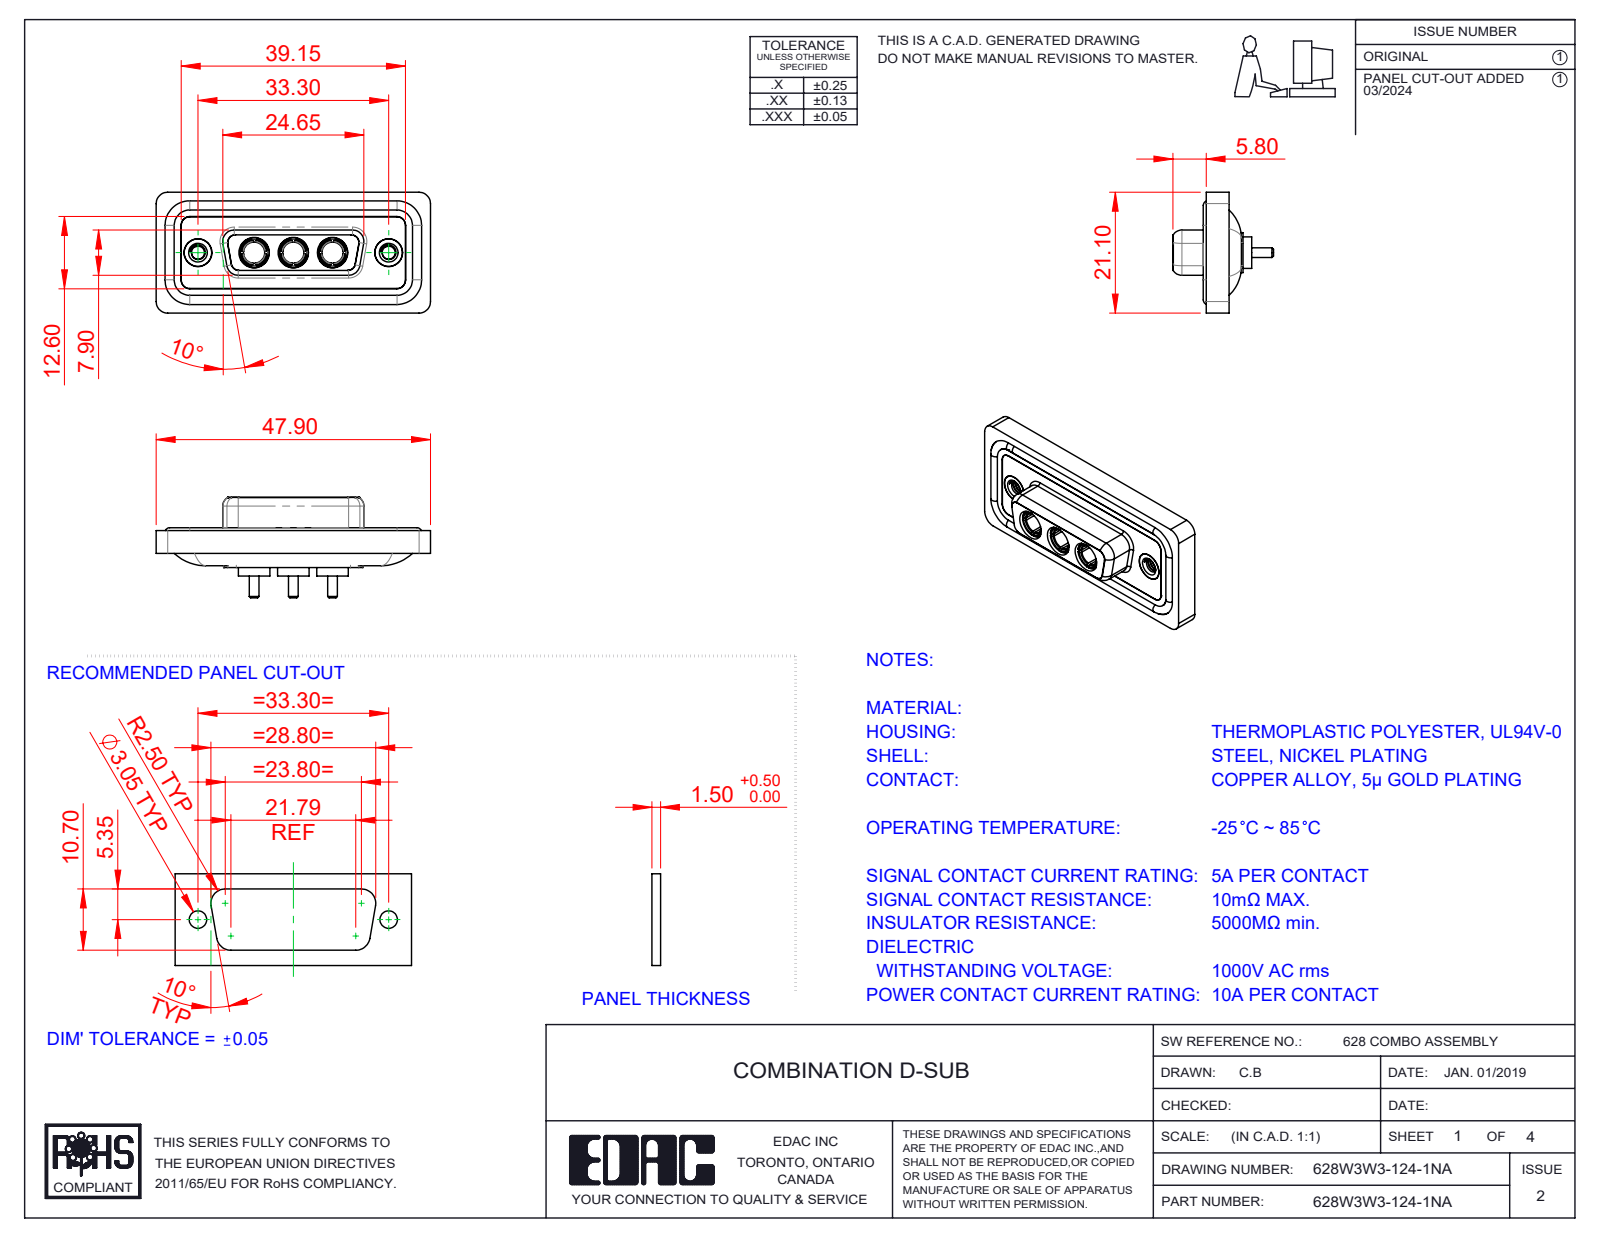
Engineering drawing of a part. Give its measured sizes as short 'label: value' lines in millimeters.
name: 628Combo Threaded Rivet_A; 628Combo Housing_3W3; 628Combo Waterproof Housing_15 Contacts; 628W3W3-124-1NA (+3 more)
written by: SolidWorks 2023 (CONFIG_CONTROL_DESIGN)
unit: mm
bodies: 13 solids, 606 faces (192 planar, 259 cylindrical, 155 other)
size: 47.9 × 21.1 × 17.55
volume: 5 984 mm³; area: 9 698 mm²
holes: 5× ⌀4.85, 3× ⌀3.7, 3× ⌀5.3, 2× ⌀2.26, 2× ⌀4, 2× ⌀4.05, 2× ⌀5
bosses: 4× ⌀1.6, 3× ⌀5.5, 3× ⌀5.2, 3× ⌀4.96, 3× ⌀4.75, 3× ⌀3.75, 3× ⌀1.7, 2× ⌀4.95
rounds: 22× R1.5, 20× R2, 12× R1.35, 8× R1.6, 4× R0.25, 4× R0.5, 4× R0.6, 4× R0.65
face distances: 0.4, 1.8, 1.6, 0.5, 7.45, 1.1, 2.9, 5.65, 7.05, 1.5
hole spacings: 6.85, 9.8, 16.65, 23.5, 13.7, 33.3
